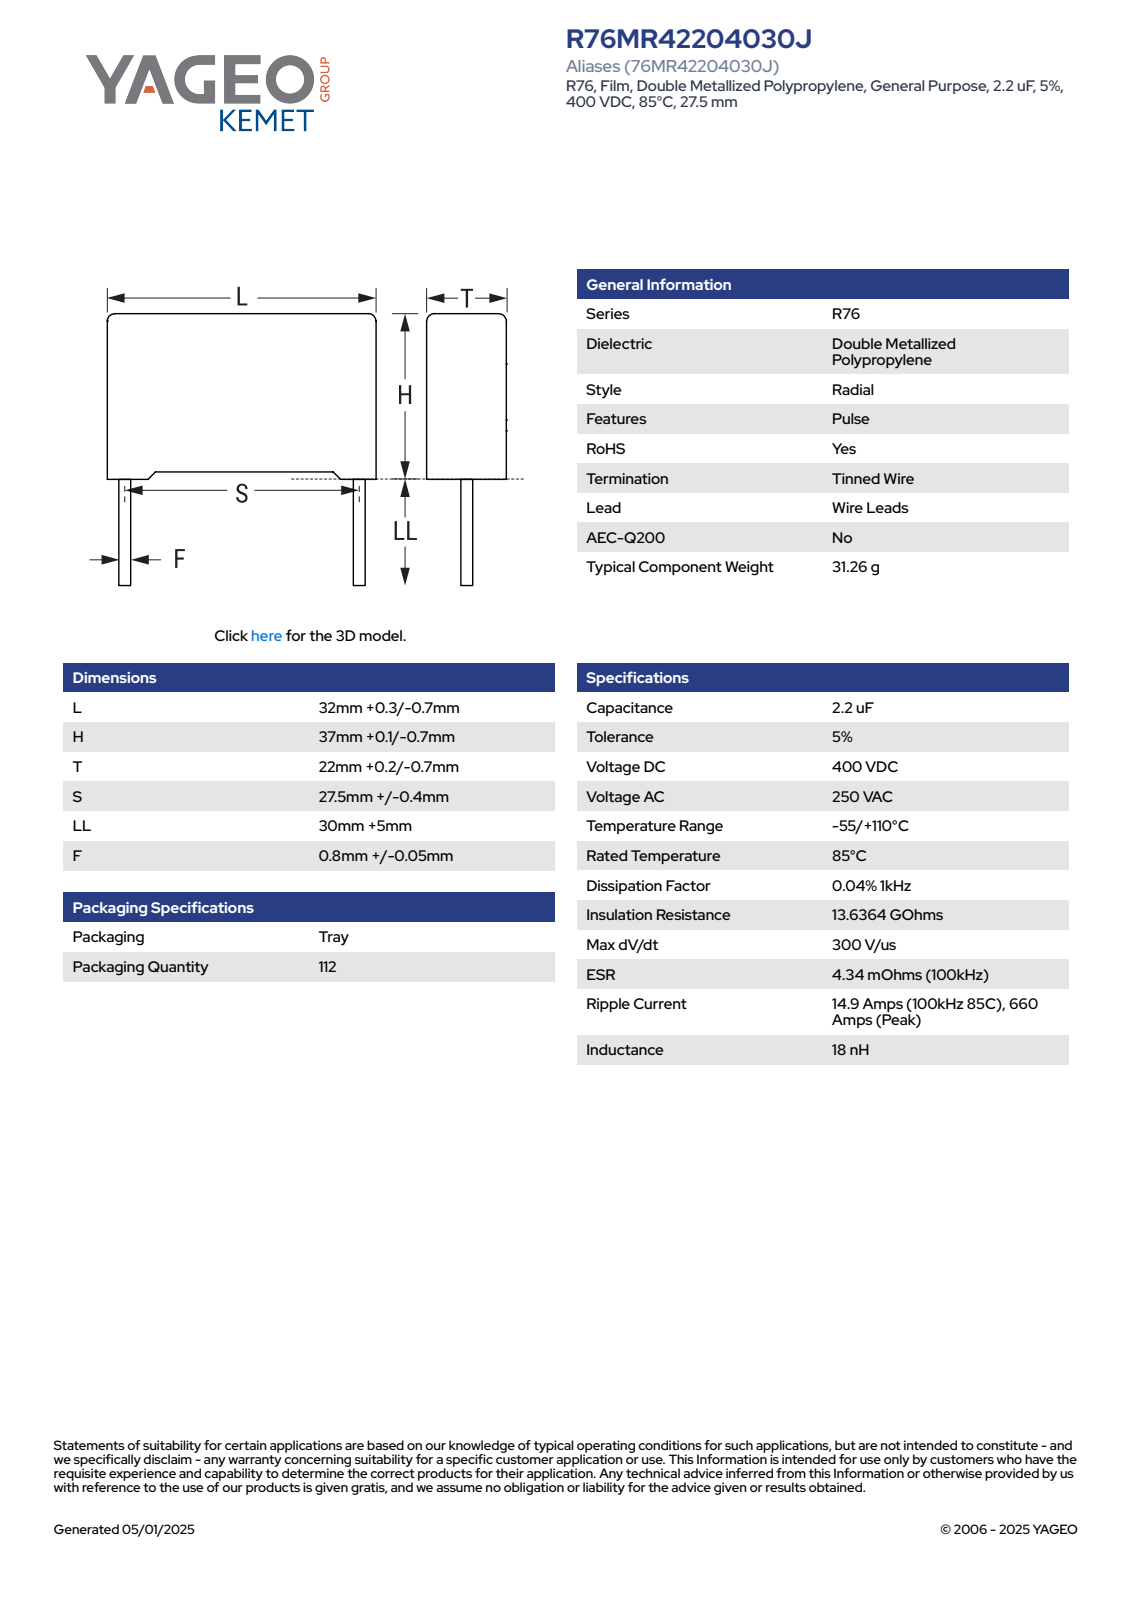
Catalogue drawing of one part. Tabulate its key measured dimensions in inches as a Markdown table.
| quantity | value |
| --- | --- |
| part name | CFR_RB2_32X37X22_L32.3H37.1T22.2S27.5LL35F0.85 |
| STEP written by | SolidWorks 2021 (AUTOMOTIVE_DESIGN) |
| units | inches |
| bodies | 4 solids, 85 faces (77 planar, 8 cylindrical, 0 other) |
| overall size | 2.839 × 1.272 × 0.874 |
| volume | 1.579 in³ |
| surface area | 8.86 in² |
| round bosses / shafts (diameter × count) | 0.033 × 2 |
| partial cylindrical surfaces (radius × count) | 0.02 × 4 |
| main face-to-face distances | 0.874, 1.272, 1.41, 0.021, 1.431, 0.03, 0.05, 1.461, 0.043, 1.229 |
